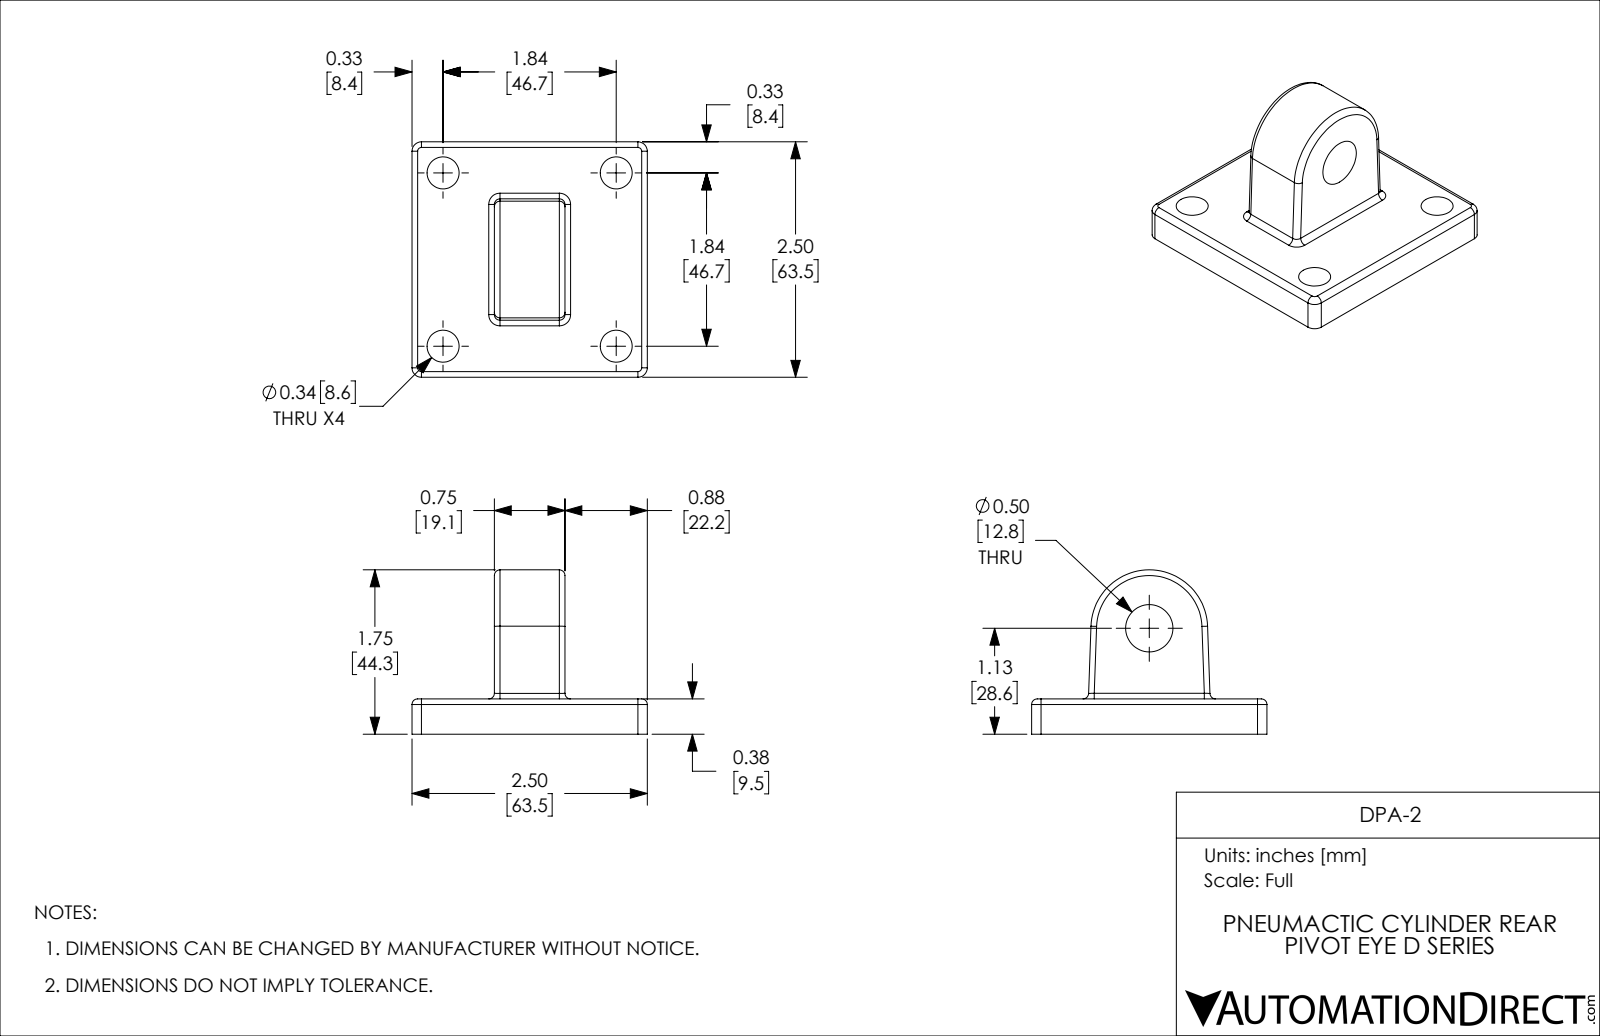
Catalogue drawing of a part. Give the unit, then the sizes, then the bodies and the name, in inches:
Units: inches
Overall size (bounding box): 2.5 × 2.5 × 1.745
Round holes (diameter × count): ⌀0.34 ×4, ⌀0.502 ×1
Partial cylindrical surfaces — rounded edges, fillets, slot ends (radius × count): R0.06 ×12, R0.1 ×4, R0.62 ×1
Main face-to-face distances: 0.375, 2.5, 0.875, 1.625, 0.75
Hole centre spacings: 1.84, 2.602
Volume: 3.212 in³ · Surface area: 22.03 in²
Bodies: 1 solid, 48 faces (10 planar, 28 cylindrical, 10 other)
Part name (STEP PRODUCT): DPA-2
STEP written by: SolidWorks 2018 (AUTOMOTIVE_DESIGN)
